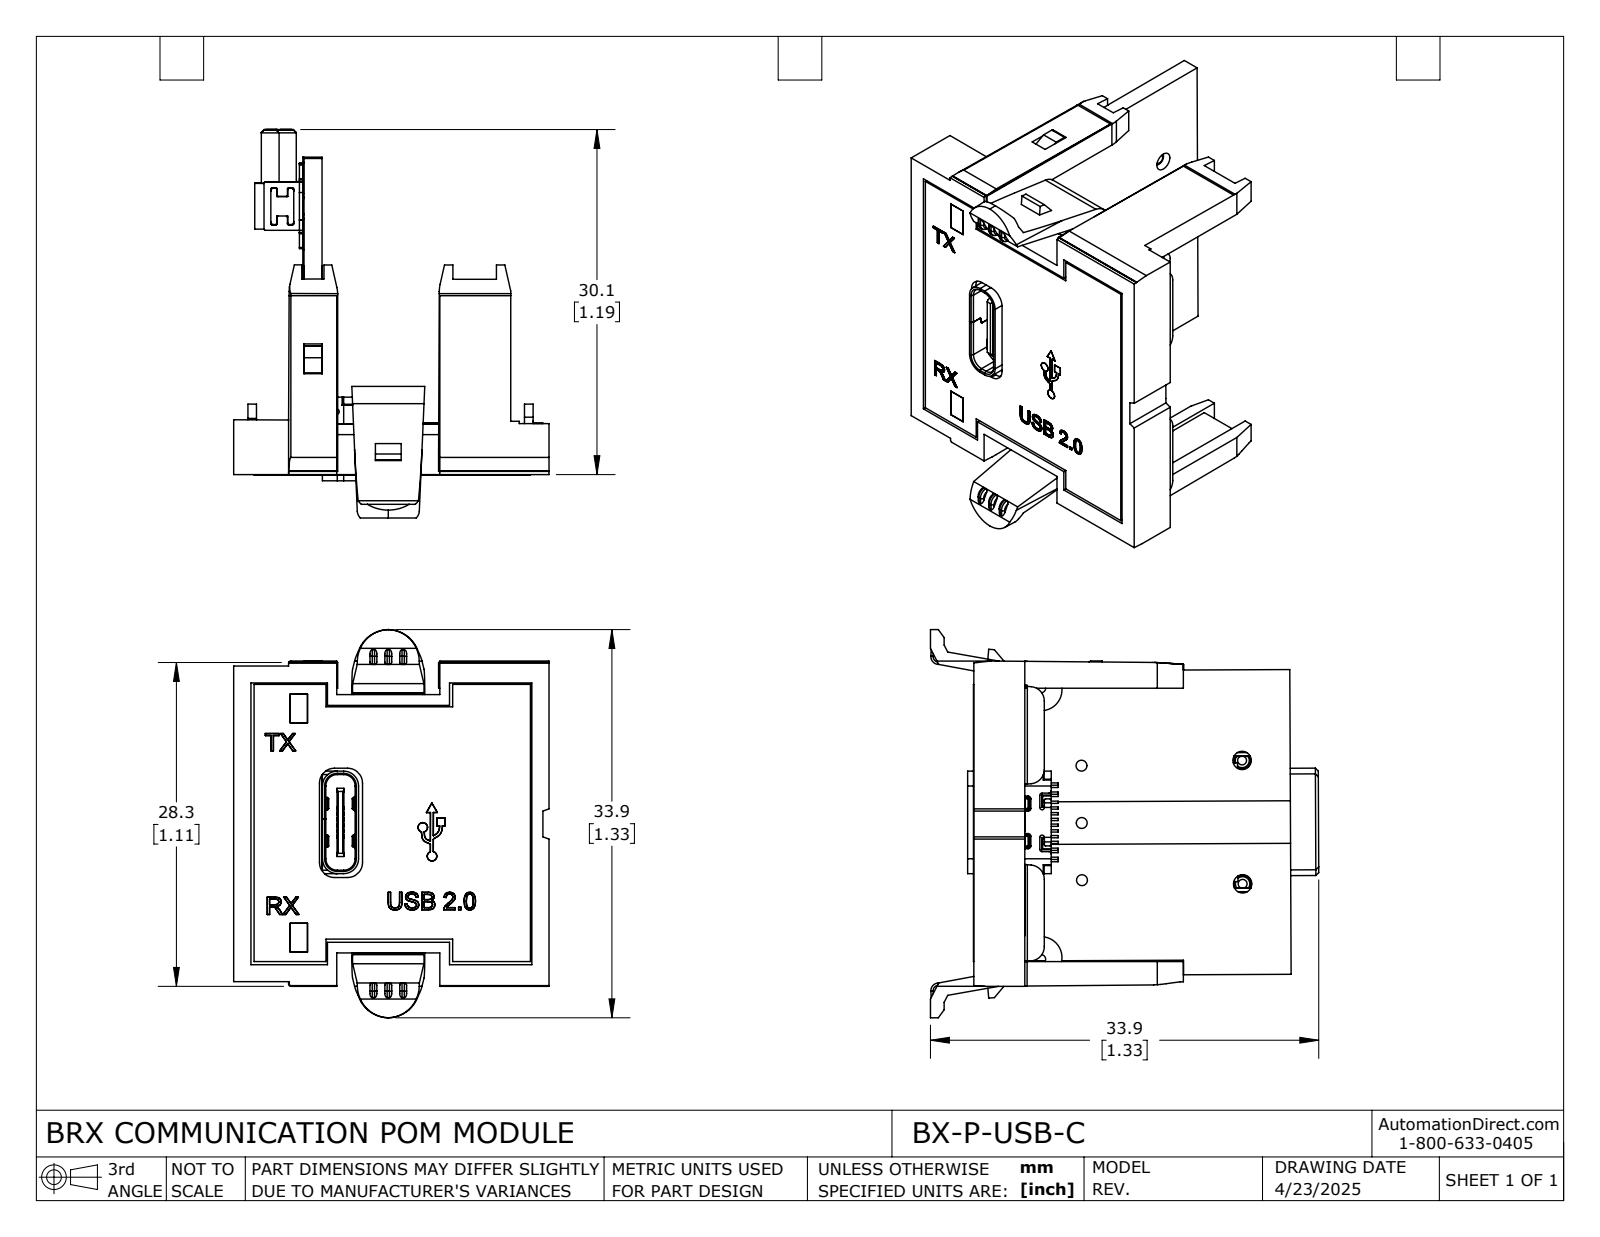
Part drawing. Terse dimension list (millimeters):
name: BX-P-USB-C
written by: SolidWorks 2021 (AUTOMOTIVE_DESIGN)
unit: mm
bodies: 27 solids, 2192 faces (1483 planar, 346 cylindrical, 363 other)
size: 33.9 × 33.9 × 27.5
volume: 3 740 mm³; area: 7 348 mm²
holes: 3× ⌀0.9, 2× ⌀1.6
bosses: 2× ⌀0.5
rounds: 50× R0.1, 44× R0.1, 35× R0.2, 8× R0.2, 8× R0.2, 8× R0.3, 7× R1, 5× R0.5
face distances: 0.5, 1.6, 1.7, 0.5, 1.7, 1.6, 0.5, 27.5, 6, 6.1
hole spacings: 14, 17.4, 5, 5, 10, 10.8, 15, 15
